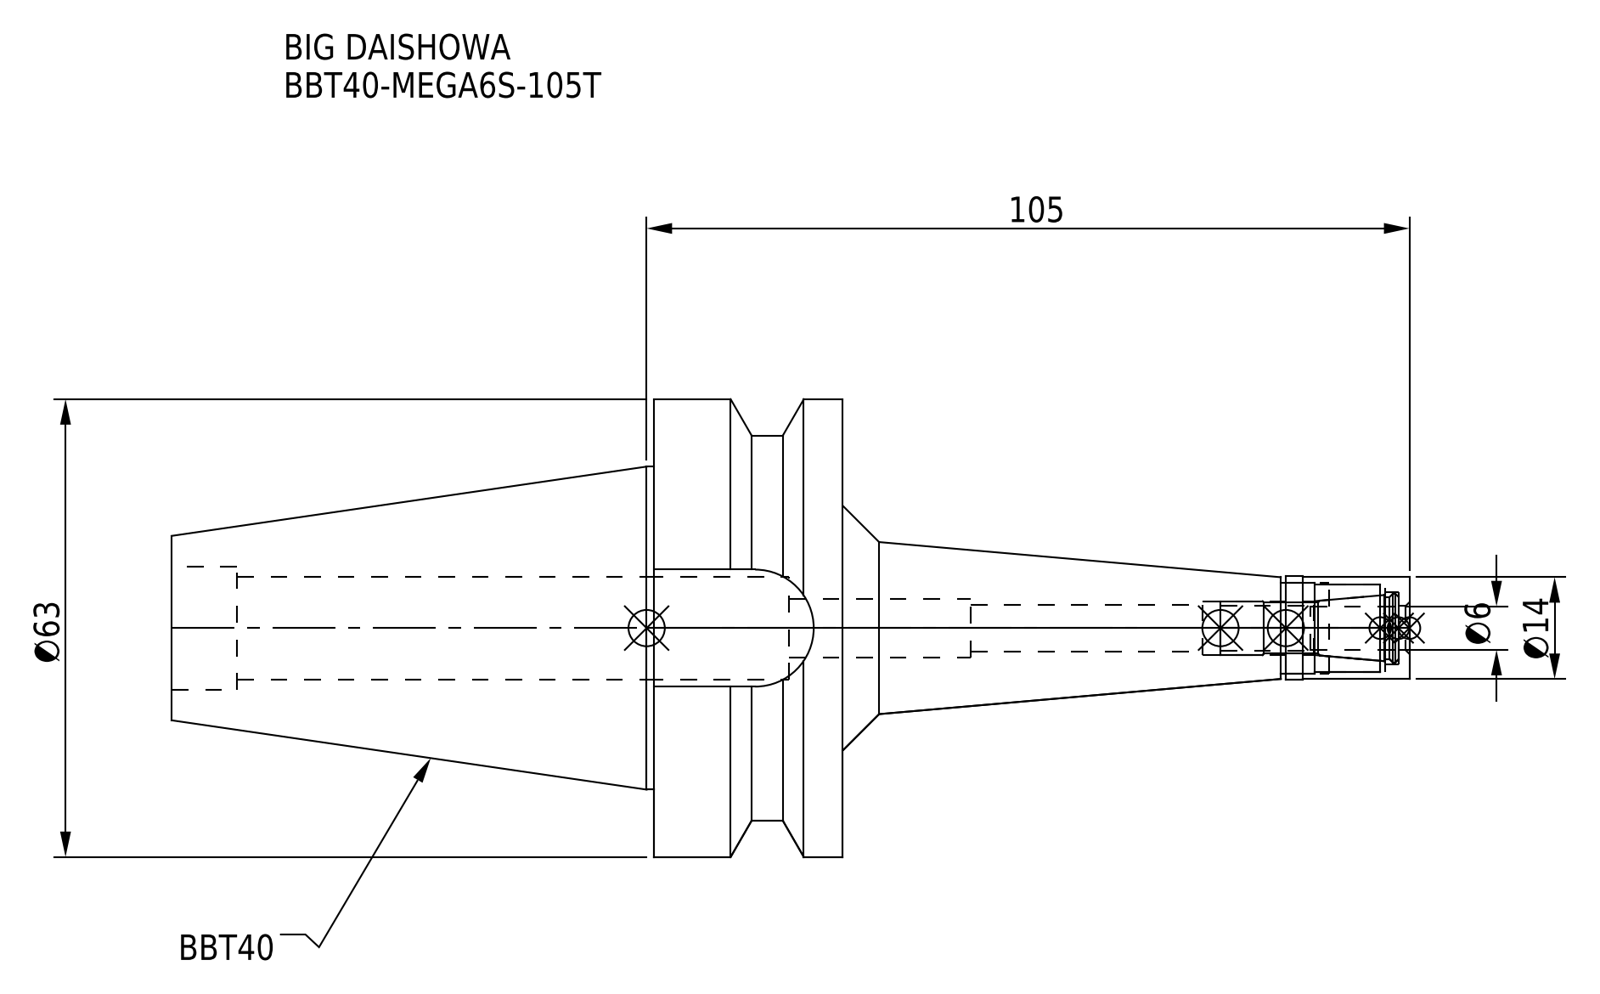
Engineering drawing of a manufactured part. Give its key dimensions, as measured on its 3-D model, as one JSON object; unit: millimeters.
{"part_name": "BBT40-MEGA6S-105T_1.stp; DXF_TEMP_ASSY_ASM_4_ASM.stp; BBT40-MEGA6S-105T; BBT40-MEGA6S-105T-060-FreeParts (+3 more)", "step_written_by": "SolidWorks 2019 (CONFIG_CONTROL_DESIGN)", "units": "millimeters", "bodies": {"solids": 2, "faces": 74, "planar": 22, "cylindrical": 38, "other": 14}, "overall_size": [170.4, 63, 63], "volume_mm3": 139519, "surface_area_mm2": 29789, "round_holes": [[6.1, 1], [6.4, 1], [7.4, 1], [8, 1], [10, 1], [12, 1], [12.5, 1], [14.2, 1], [17, 1]], "round_bosses_or_shafts": [[63, 1], [53, 1], [44.45, 1], [14.3, 1], [14, 1]], "partial_cylinders_radius": [[8.05, 1]], "face_to_face_distances": [26, 45, 92.4, 66.4, 16.1, 78, 104, 170.4, 85.4, 7.4]}
